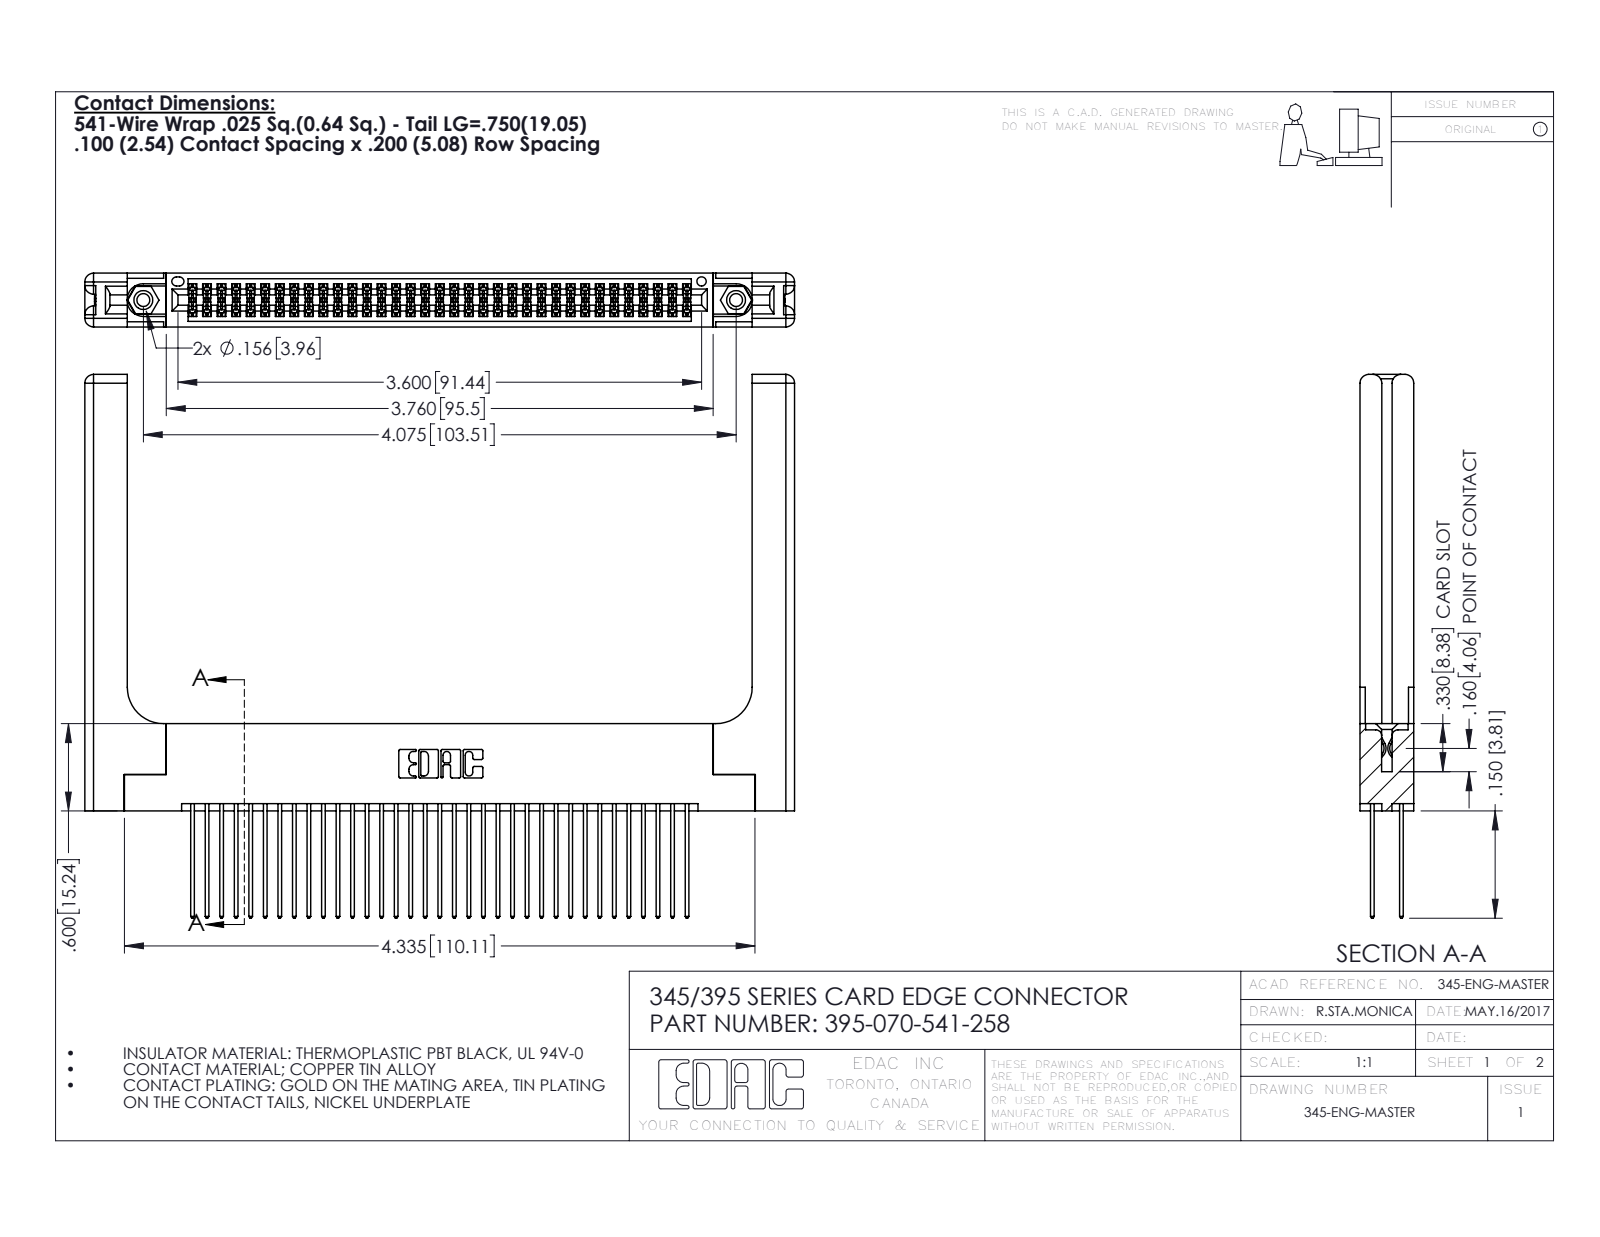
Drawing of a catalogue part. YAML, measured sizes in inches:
part_name: "345-292-001_345-293-141; 345 Part_Flush Mounting Lugs - 0.156 Dia-TH; 345-220-058_345-220-058; 395-070-541-258 (+1 more)"
step_written_by: "SolidWorks 2016 (CONFIG_CONTROL_DESIGN)"
units: inches
bodies: {solids: 75, faces: 3882, planar: 2538, cylindrical: 1284, other: 60}
overall_size: [4.879, 3.737, 0.37]
volume: 1.272
surface_area: 38.91
round_holes:
  - {diameter: 0.089, count: 2}
  - {diameter: 0.125, count: 2}
  - {diameter: 0.156, count: 2}
  - {diameter: 0.064, count: 1}
round_bosses_or_shafts:
  - {diameter: 0.155, count: 2}
partial_cylinders:
  - {radius: 0.006, count: 105}
  - {radius: 0.01, count: 70}
  - {radius: 0.01, count: 22}
  - {radius: 0.06, count: 16}
  - {radius: 0.007, count: 6}
  - {radius: 0.031, count: 6}
  - {radius: 0.026, count: 3}
  - {radius: 0.014, count: 2}
face_to_face_distances: [0.072, 0.298, 0.37, 0.2, 0.098, 0.272, 0.025, 0.225, 0.175, 0.148]
hole_center_spacings: [0.27, 3.839, 4.075]
